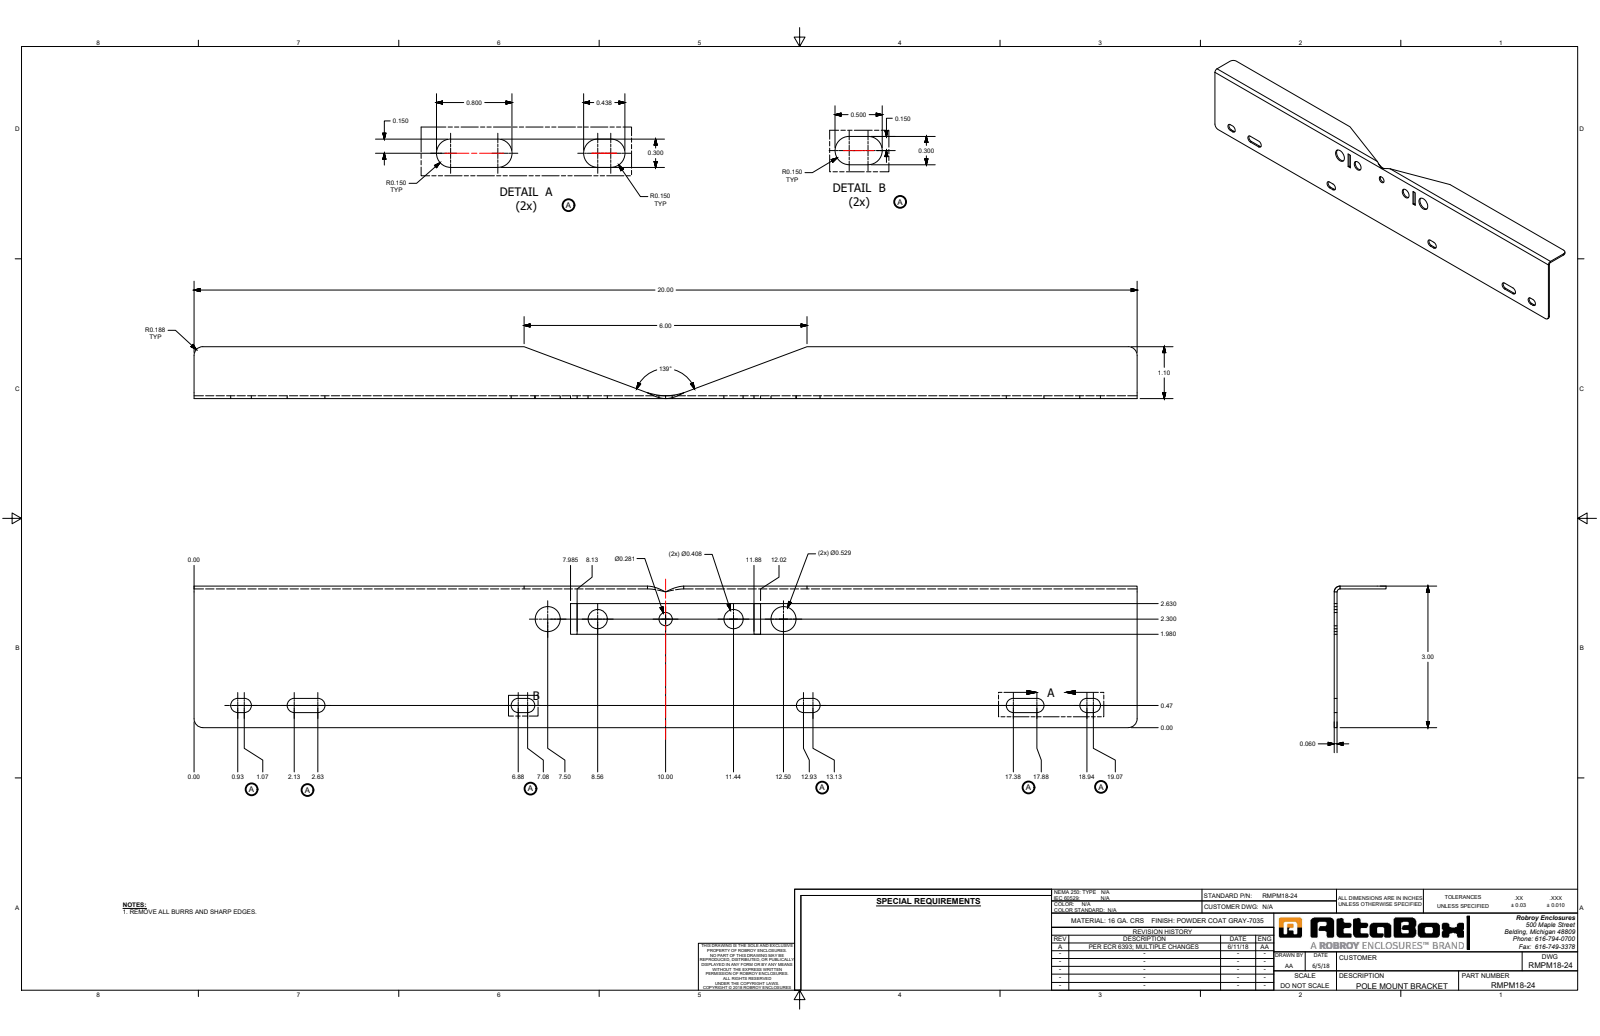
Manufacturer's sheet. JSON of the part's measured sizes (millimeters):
{"part_name": "PM18-24", "step_written_by": "SolidWorks 2019 (AUTOMOTIVE_DESIGN)", "units": "millimeters", "bodies": {"solids": 1, "faces": 64, "planar": 37, "cylindrical": 25, "other": 2}, "overall_size": [508, 76.2, 27.9], "volume_mm3": 73480, "surface_area_mm2": 99030, "round_holes": [[10.4, 2], [13.4, 2], [7.1, 1]], "partial_cylinders_radius": [[3.8, 12], [4.7, 2], [4.8, 2], [1.6, 1], [3.1, 1]], "face_to_face_distances": [1.5, 74.7, 76.2, 26.4, 27.9, 508, 15.7, 58.9, 60.5, 8.1], "hole_center_spacings": [26.9, 36.6, 63.5, 100.1, 73.2, 127]}
